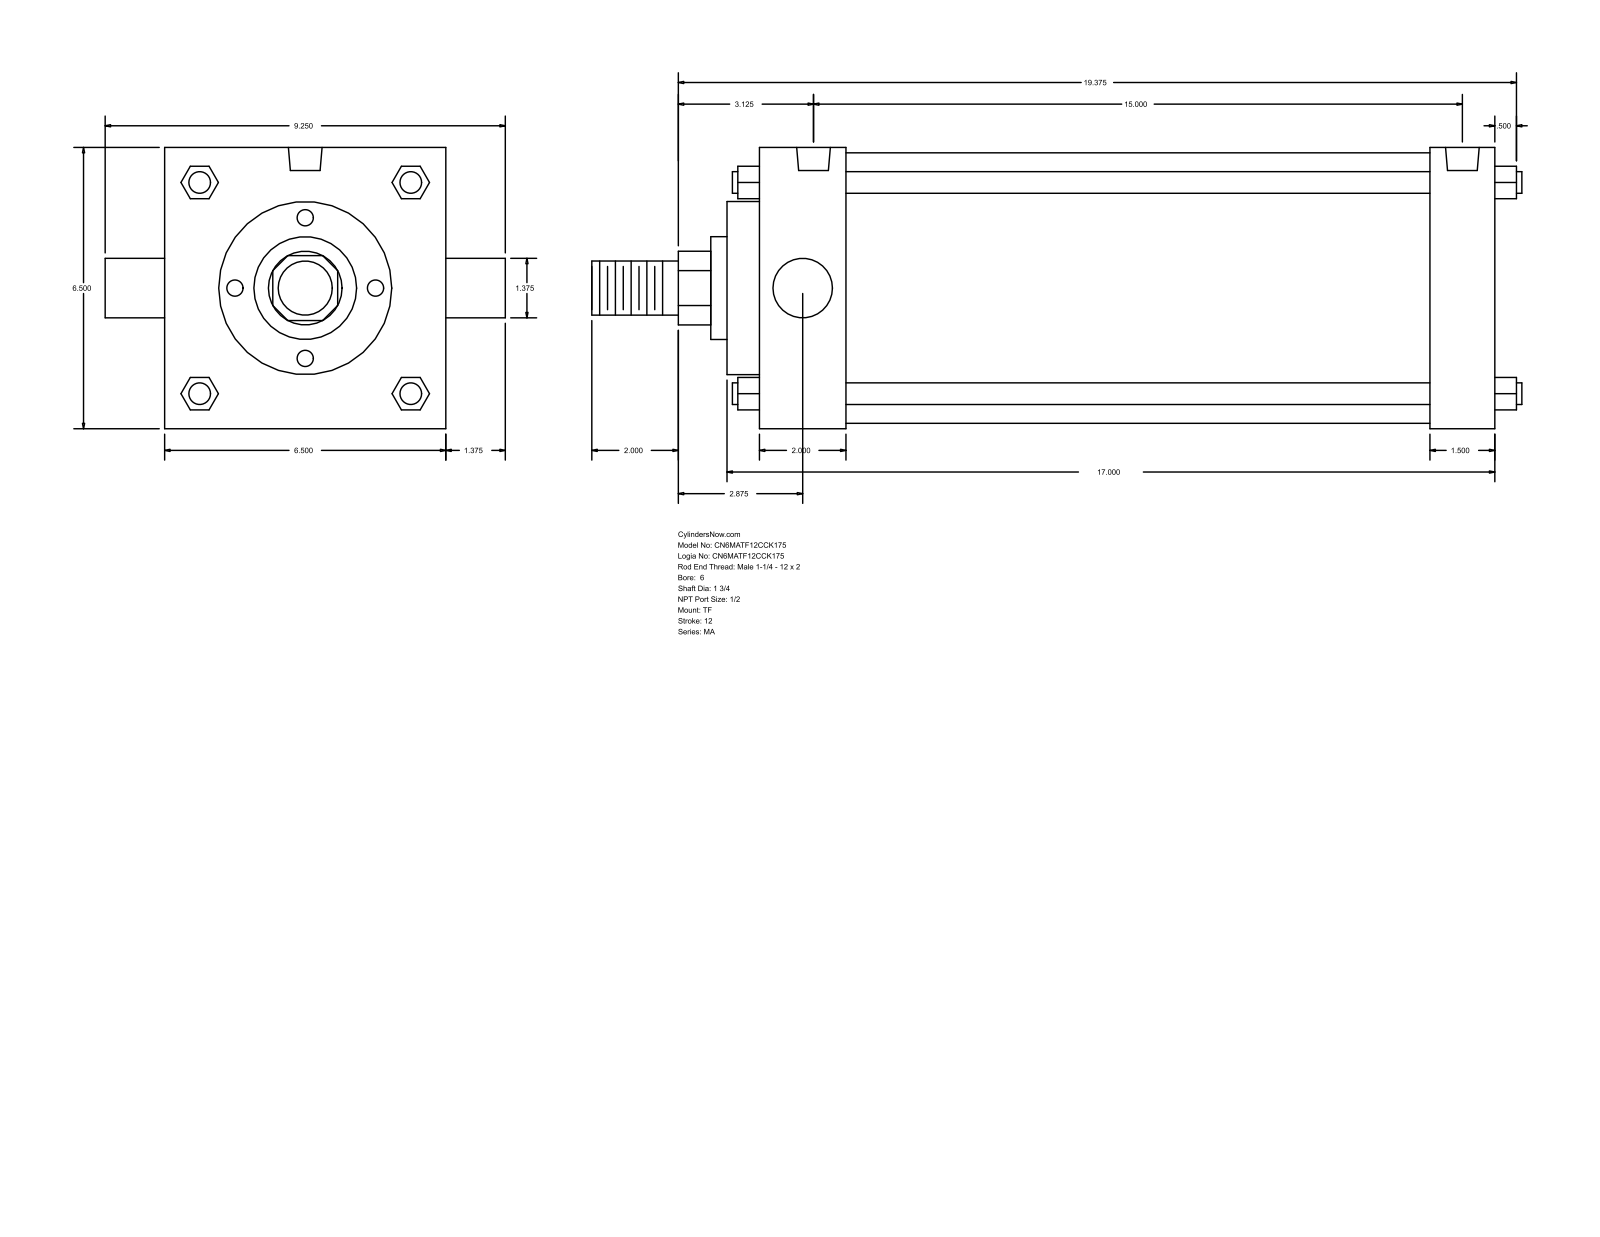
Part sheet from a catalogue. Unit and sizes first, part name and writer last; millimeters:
Units: millimetres
Overall size (bounding box): 546.1 × 234.95 × 165.1
Round holes (diameter × count): ⌀17.46 ×3, ⌀19.77 ×2
Round bosses / shafts (diameter × count): ⌀12.7 ×4, ⌀158.75 ×1, ⌀101.6 ×1, ⌀60.33 ×1, ⌀44.45 ×1, ⌀34.92 ×1, ⌀31.75 ×1
Partial cylindrical surfaces — rounded edges, fillets, slot ends (radius × count): R21.63 ×1
Main face-to-face distances: 165.1, 431.81, 19.05, 50.8, 393.7, 381.01, 342.9, 38.11, 69.85, 412.75
Hole centre spacings: 381
Bodies: 0 solids, 122 faces (93 planar, 29 cylindrical, 0 other)
Part name (STEP PRODUCT): MA_TF__0600_1.75
STEP written by: GSSL Pune (CONFIG_CONTROL_DESIGN)
